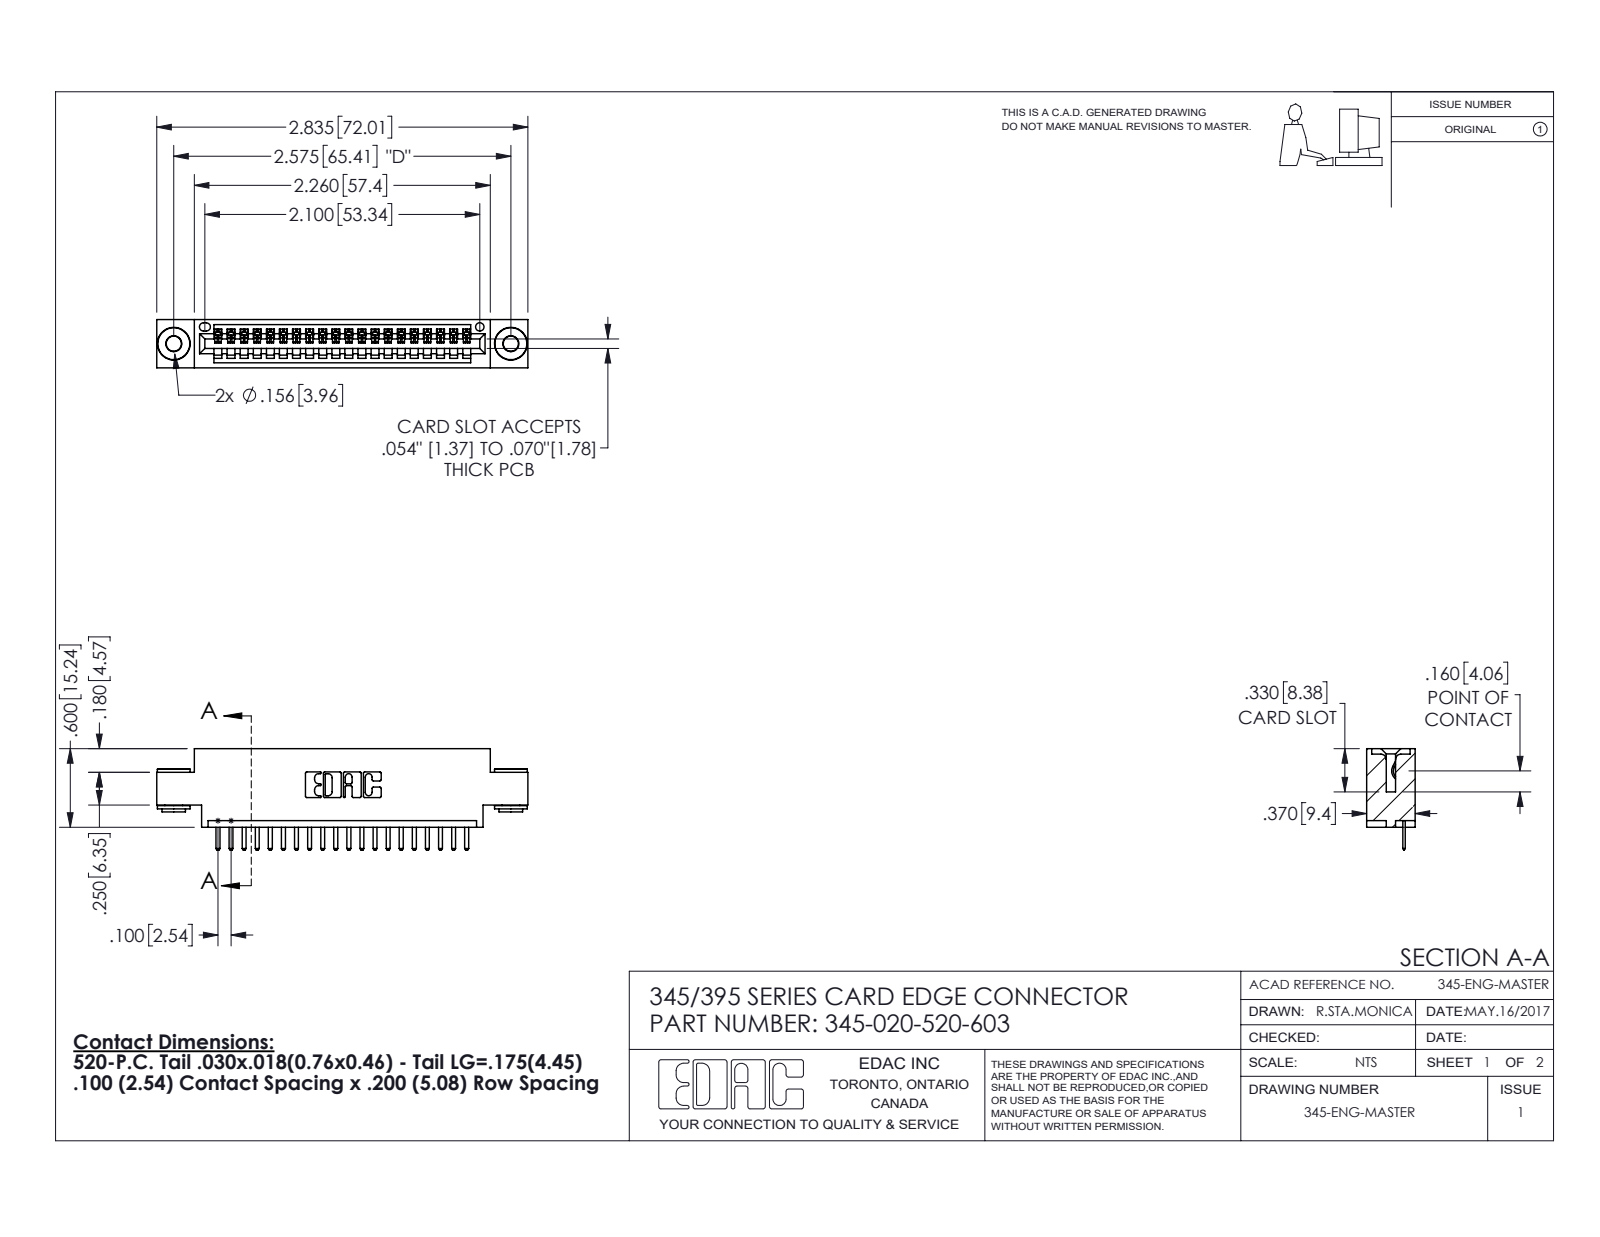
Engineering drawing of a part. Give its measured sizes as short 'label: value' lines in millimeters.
name: 345-020-520-603; 345-250-002_345-250-002-102; 345-292-001_345-293-120; 345 Part_0.170 Offset - 0.156 Dia-TH
written by: SolidWorks 2016 (CONFIG_CONTROL_DESIGN)
unit: mm
bodies: 23 solids, 1408 faces (934 planar, 466 cylindrical, 8 other)
size: 72 × 19.7 × 9.4
volume: 6 510 mm³; area: 8 503 mm²
holes: 2× ⌀2.9, 2× ⌀4, 1× ⌀1.6
bosses: 2× ⌀6.4, 2× ⌀4.6, 2× ⌀3.5
rounds: 42× R0.3, 40× R0.2, 22× R0.3, 6× R0.2, 6× R0.8, 3× R0.7, 2× R0.8, 2× R1
face distances: 9.4, 1.8, 7.6, 5.1, 2.5, 6.9, 0.6, 5.7, 4.4, 2.5
hole spacings: 6.9, 59.5, 65.4
